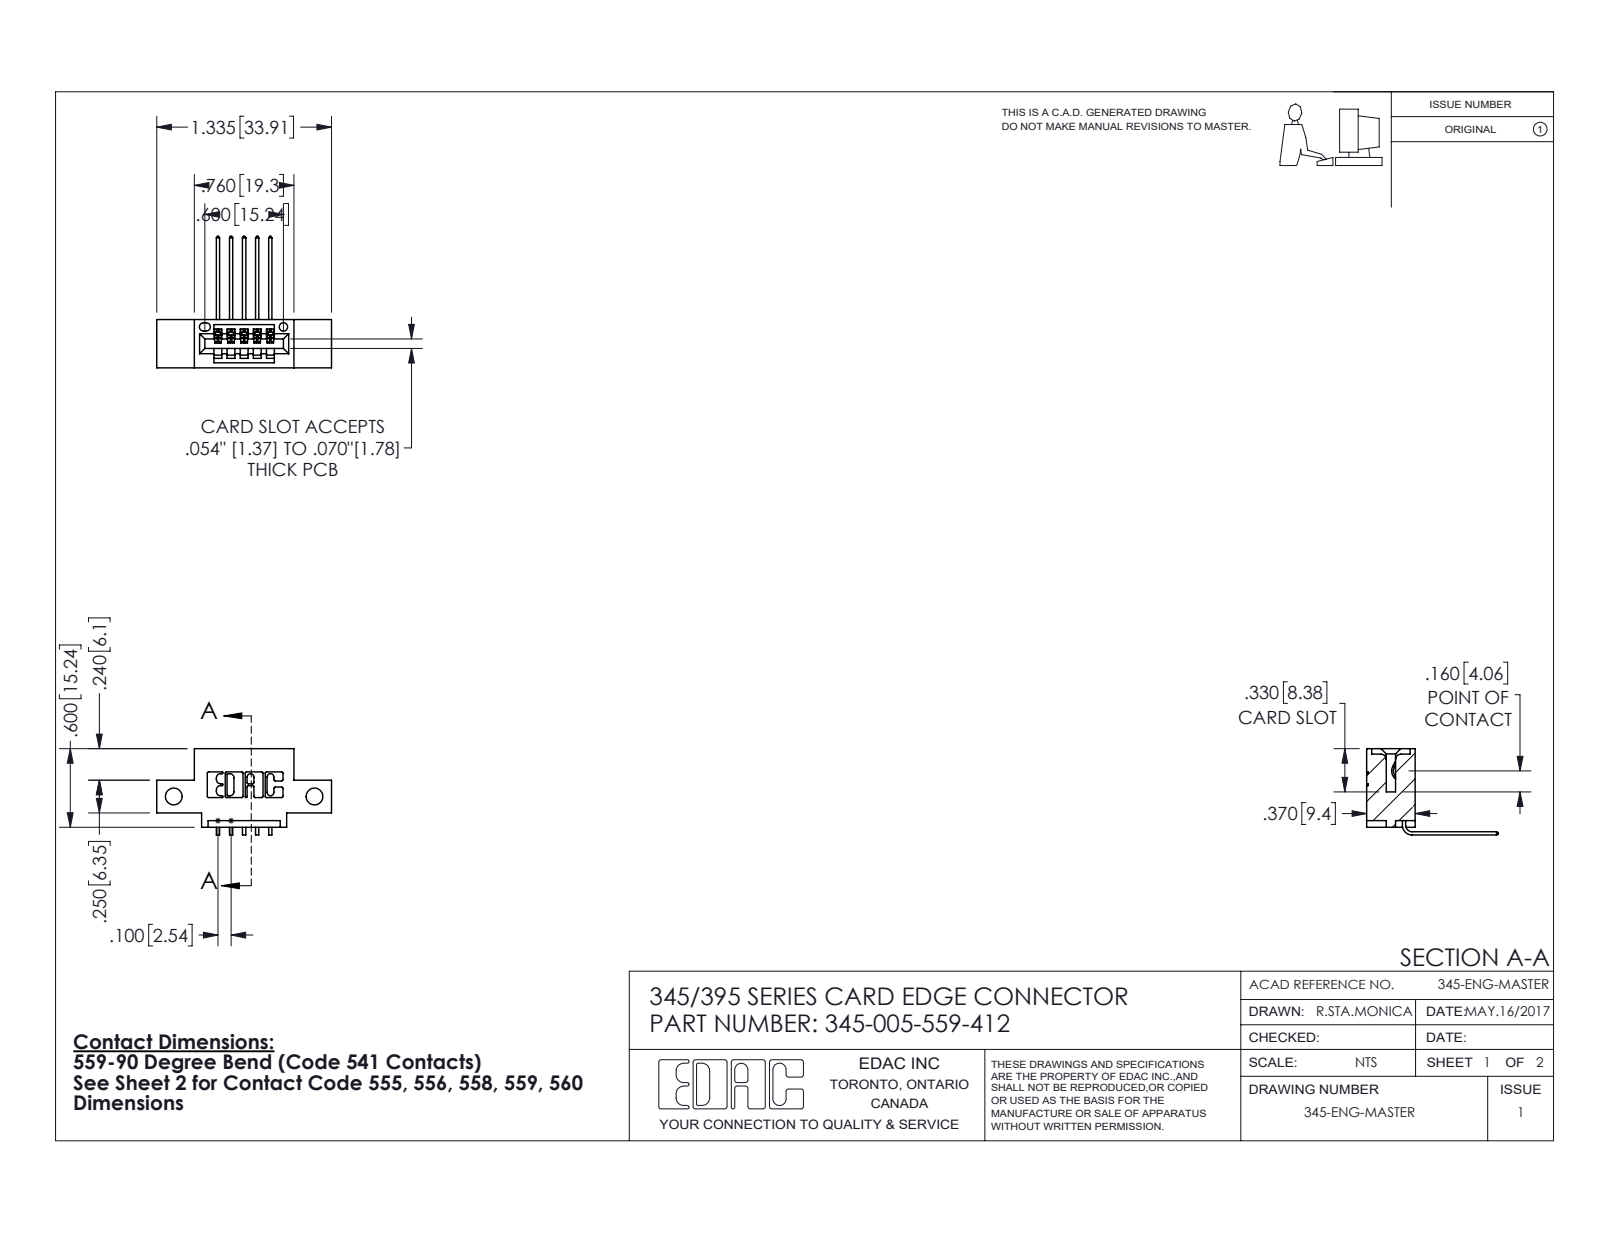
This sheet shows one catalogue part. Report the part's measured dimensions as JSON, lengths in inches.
{"part_name": "345 Part_0.110 Offset - Side Mount; 345-292-001_558 559 Tail - 1; 345-005-559-412", "step_written_by": "SolidWorks 2016 (CONFIG_CONTROL_DESIGN)", "units": "inches", "bodies": {"solids": 6, "faces": 430, "planar": 294, "cylindrical": 136, "other": 0}, "overall_size": [1.335, 1.005, 0.659], "volume_in3": 0.169, "surface_area_in2": 4.992, "round_holes": [[0.128, 2], [0.064, 1]], "partial_cylinders_radius": [[0.01, 22], [0.006, 10], [0.007, 6], [0.031, 6], [0.026, 3], [0.031, 2], [0.04, 2], [0.014, 1]], "face_to_face_distances": [0.2, 0.37, 0.1, 0.072, 0.298, 0.25, 0.025, 0.06, 0.16, 0.098], "hole_center_spacings": [1.075]}
